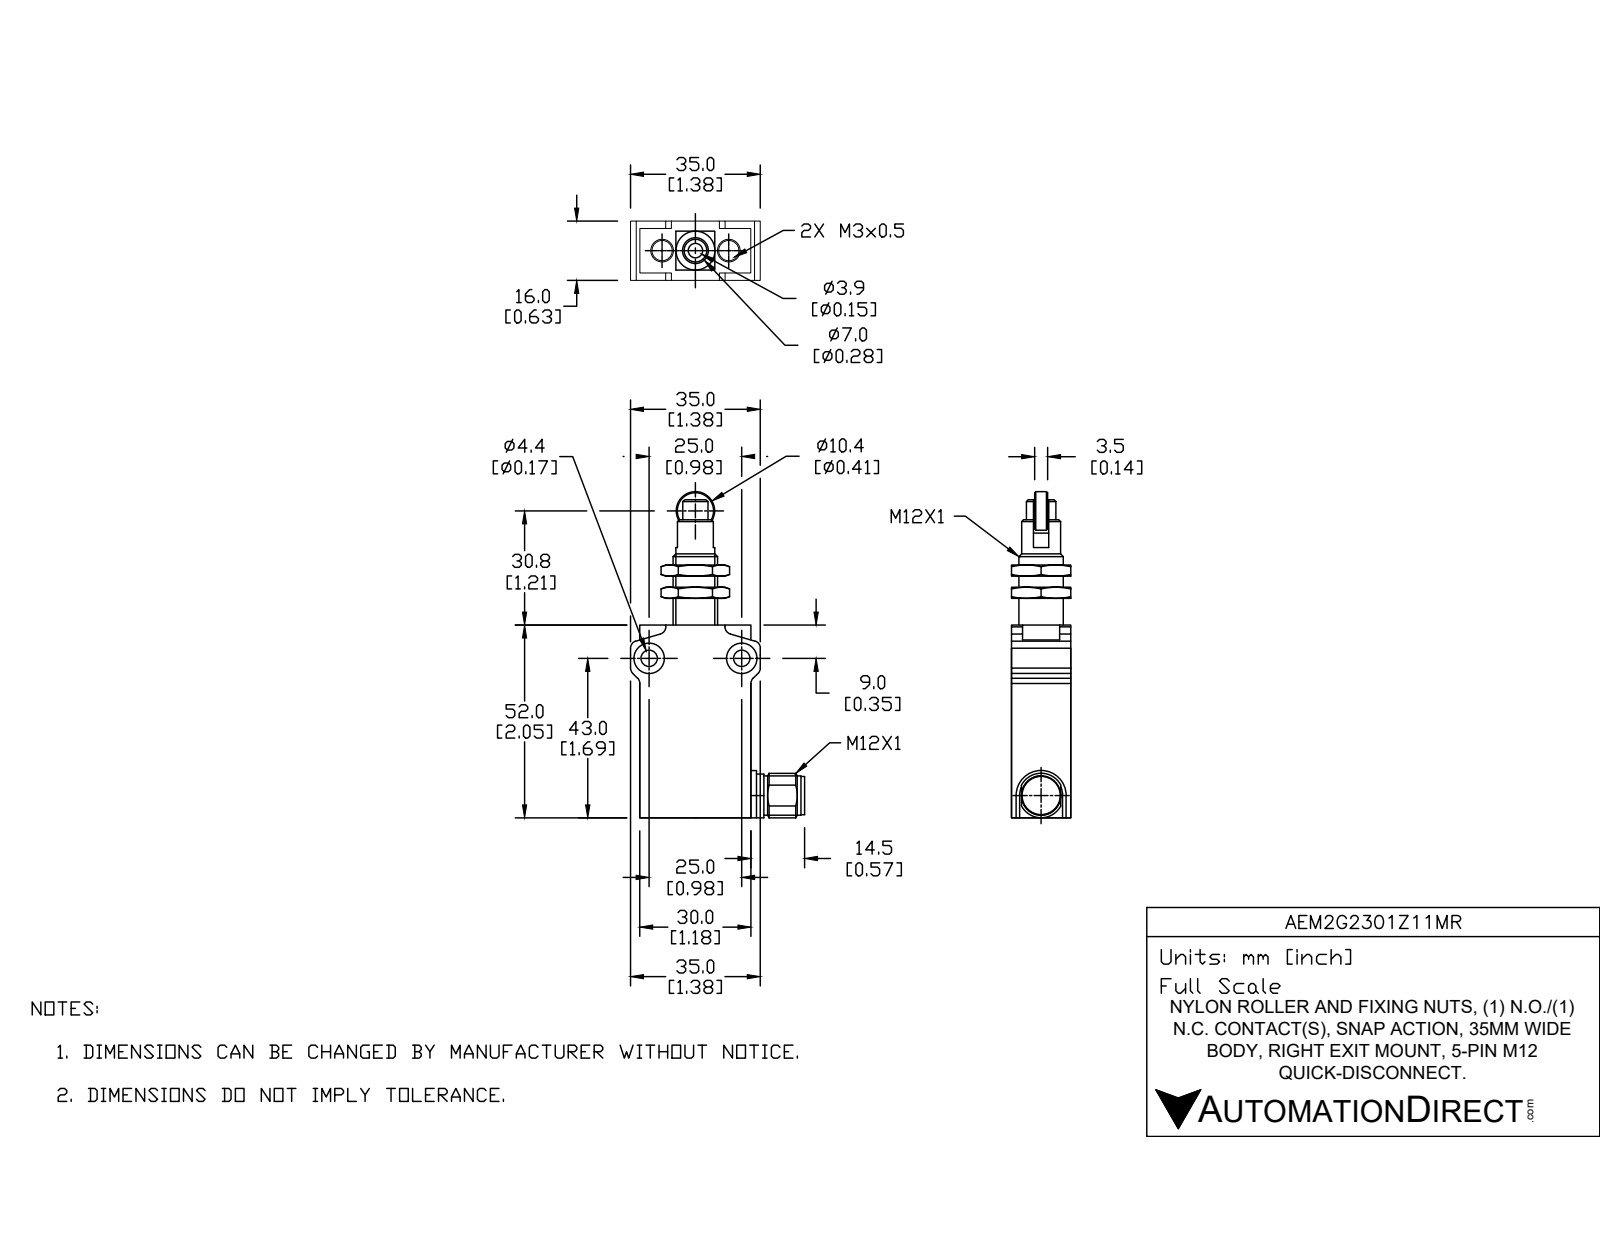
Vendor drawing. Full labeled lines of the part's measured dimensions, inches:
Part name (STEP PRODUCT): AEM2G2301Z11MR
STEP written by: SolidWorks 2019 (AUTOMOTIVE_DESIGN)
Units: inches
Bodies: 7 solids, 199 faces (83 planar, 53 cylindrical, 63 other)
Overall size (bounding box): 3.465 × 1.831 × 0.63
Volume: 1.786 in³ · Surface area: 18.39 in²
Round holes (diameter × count): ⌀0.118 ×2, ⌀0.173 ×2, ⌀0.323 ×2, ⌀0.317 ×1, ⌀0.472 ×1
Round bosses / shafts (diameter × count): ⌀0.472 ×1, ⌀0.417 ×1, ⌀0.413 ×1, ⌀0.409 ×1, ⌀0.406 ×1, ⌀0.313 ×1, ⌀0.22 ×1
Partial cylindrical surfaces — rounded edges, fillets, slot ends (radius × count): R0.079 ×8, R0.256 ×1
Main face-to-face distances: 0.63, 1.181, 0.472, 0.118, 0.236, 2.047, 1.858, 0.189, 0.354, 0.157
Hole centre spacings: 0.374, 0.748, 0.984
